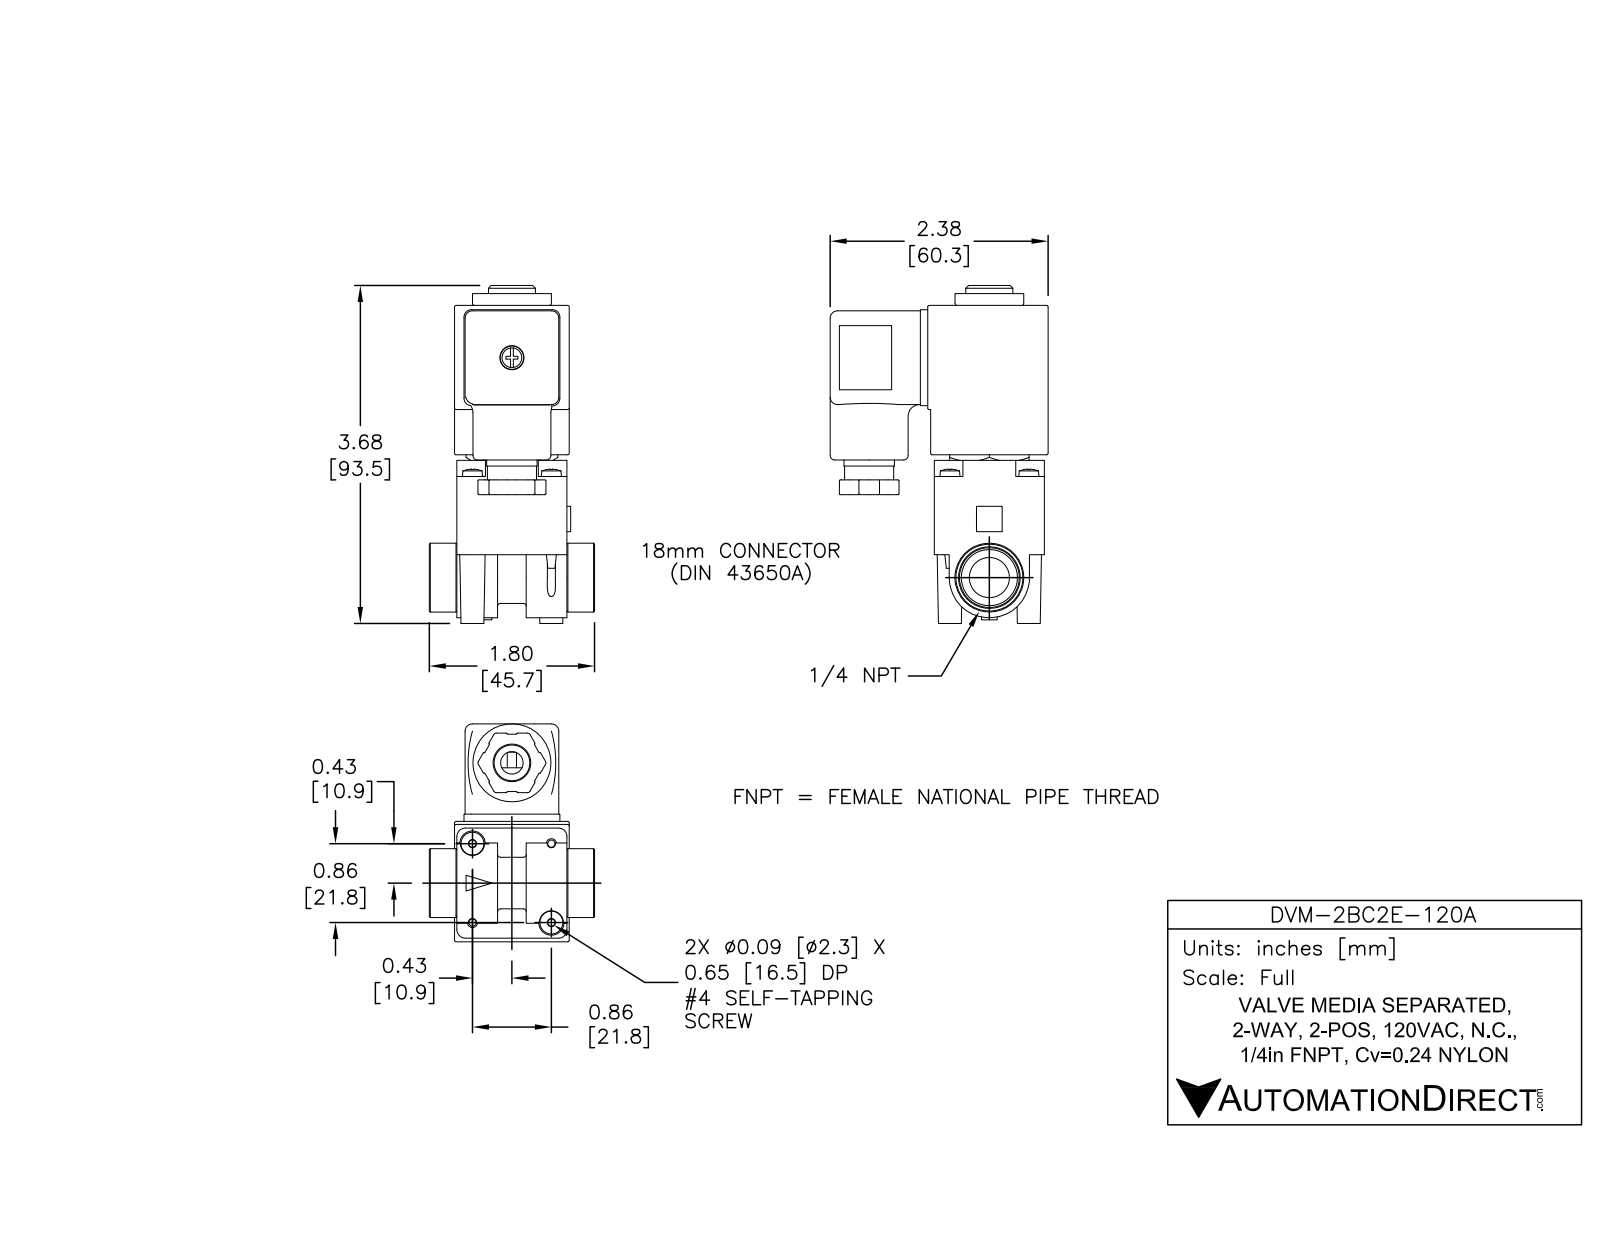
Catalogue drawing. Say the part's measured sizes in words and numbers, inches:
The part is named "DVM-2BC2E-120A". Its 3-D file was written by "SolidWorks 2015 (AUTOMOTIVE_DESIGN)". It is 14 solids with 1775 faces: 895 planar, 351 cylindrical and 529 other. Overall it measures 3.683 by 2.375 by 1.8 inches. Its volume is 5.153 cubic inches and its surface area 67.29 square inches. Round holes: 4 of diameter 0.112, 2 of diameter 0.06, 2 of diameter 0.089, 2 of diameter 0.315, 1 of diameter 0.12, 1 of diameter 0.157, 1 of diameter 0.203, 1 of diameter 0.245, 1 of diameter 0.25, 1 of diameter 0.263, 1 of diameter 0.39, 1 of diameter 0.4. Round bosses or shafts: 4 of diameter 0.217, 4 of diameter 0.125, 1 of diameter 0.85, 1 of diameter 0.807, 1 of diameter 0.75, 1 of diameter 0.68, 1 of diameter 0.535, 1 of diameter 0.52. Partial cylindrical surfaces (rounded edges, fillets, slot ends): 54 of radius 0.01, 21 of radius 0.005, 17 of radius 0.016, 12 of radius 0.02, 12 of radius 0.03, 12 of radius 0.031, 12 of radius 0.08, 8 of radius 0.05. The main face-to-face distances are 1.25, 1.2, 0.163, 1.087, 0.048, 0.974, 0.025, 1.225, 0.025, 1.225. The hole center spacings are 0.608, 0.608, 0.684, 0.86, 0.86, 0.98, 1.216, 1.457.
